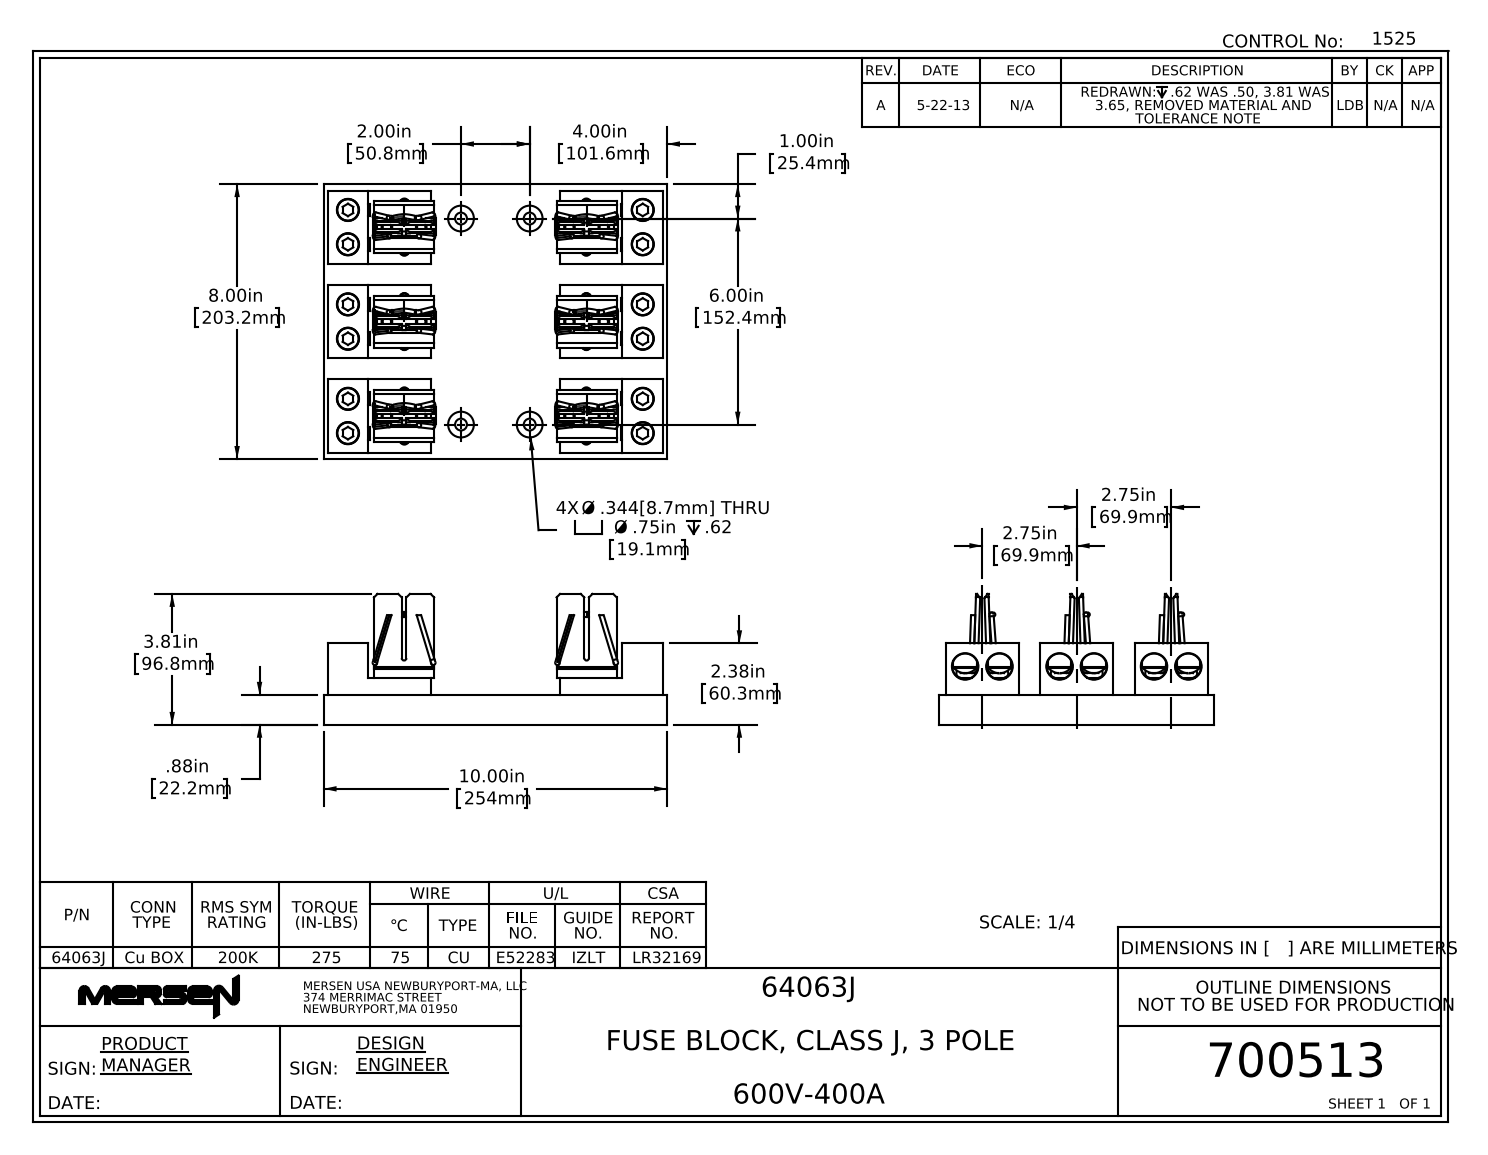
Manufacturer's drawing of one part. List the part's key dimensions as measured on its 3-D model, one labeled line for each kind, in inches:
Part name (STEP PRODUCT): 700513revA
STEP written by: SolidWorks 2017 (AUTOMOTIVE_DESIGN)
Units: inches
Bodies: 0 solids, 822 faces (460 planar, 134 cylindrical, 228 other)
Overall size (bounding box): 10 × 8 × 3.81
Round holes (diameter × count): ⌀0.266 ×12, ⌀0.85 ×12, ⌀0.75 ×10, ⌀0.625 ×5, ⌀0.344 ×4, ⌀0.625 ×1
Round bosses / shafts (diameter × count): ⌀0.688 ×12
Partial cylindrical surfaces — rounded edges, fillets, slot ends (radius × count): R0.063 ×6, R0.125 ×6, R0.187 ×6, R0.094 ×4, R0.069 ×2
Main face-to-face distances: 0.875, 2.747, 0.124, 5.494, 2.871, 2.623, 0.5, 2.75, 1.375, 2.13
Hole centre spacings: 2.75, 0.851, 4.849, 2.122, 3.474, 5.224, 5.5, 5.904
